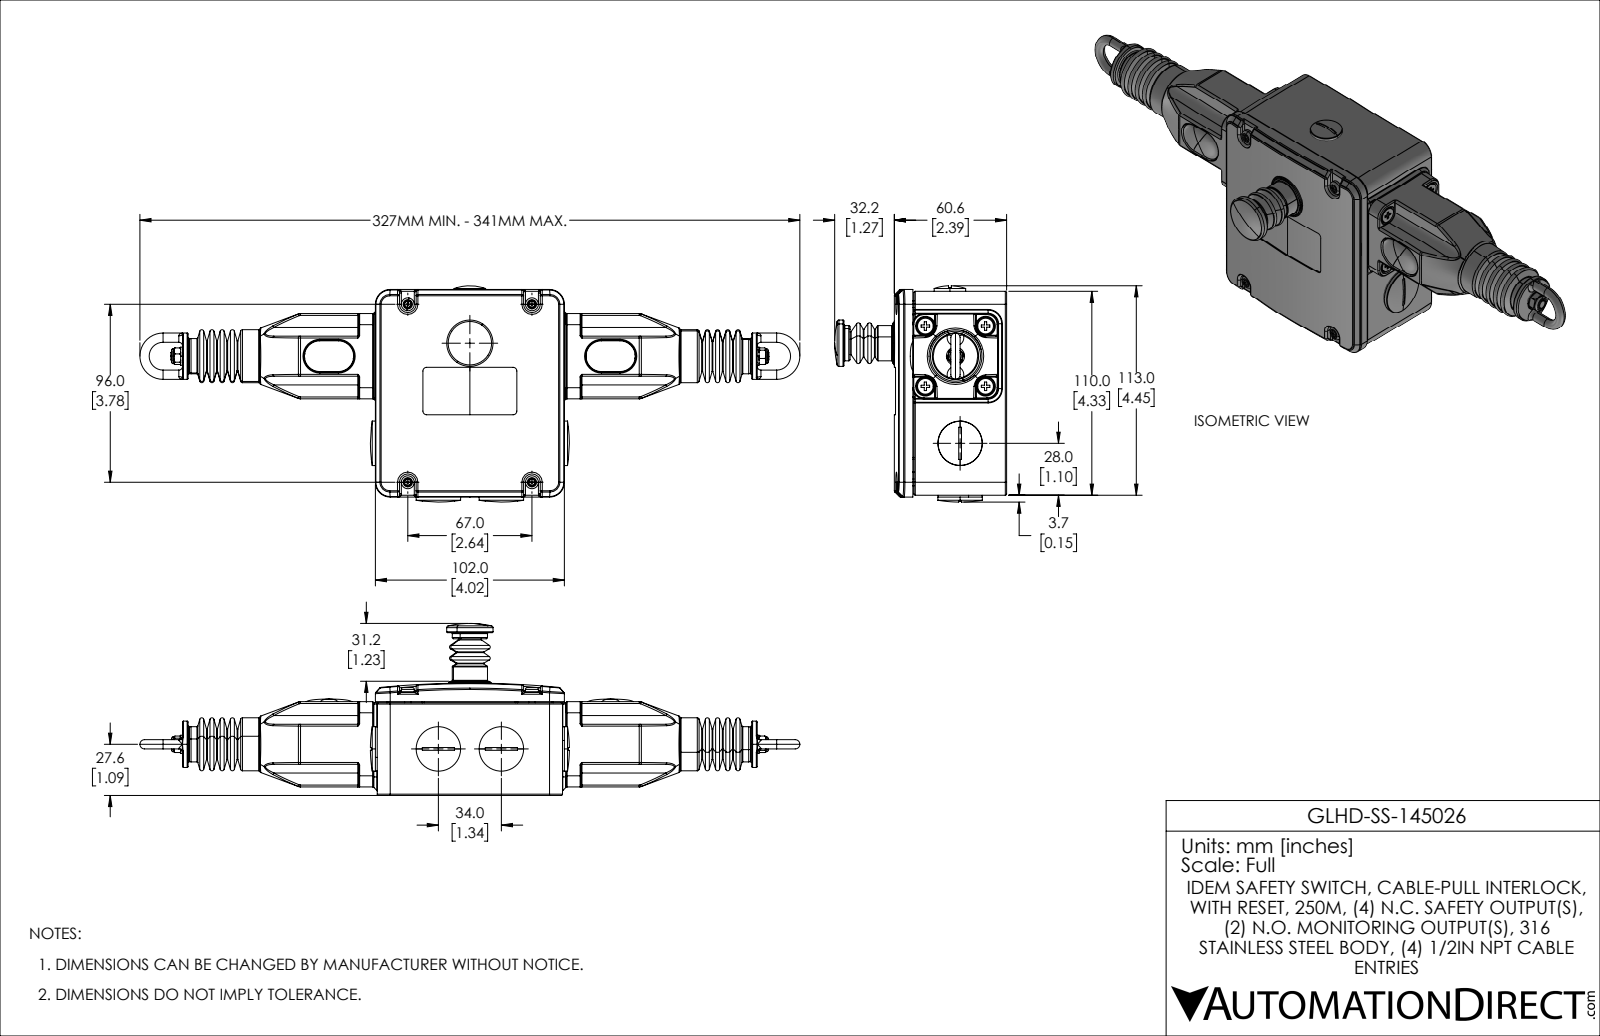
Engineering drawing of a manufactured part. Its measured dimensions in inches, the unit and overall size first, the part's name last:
Units: inches
Overall size (bounding box): 14.024 × 4.594 × 3.654
Round holes (diameter × count): ⌀0.197 ×9, ⌀0.209 ×5, ⌀0.354 ×5, ⌀0.094 ×4, ⌀0.13 ×4, ⌀0.157 ×4, ⌀0.161 ×4, ⌀0.189 ×4, ⌀0.213 ×4, ⌀0.228 ×4, ⌀0.378 ×4, ⌀0.118 ×3
Round bosses / shafts (diameter × count): ⌀0.197 ×7, ⌀0.276 ×5, ⌀0.335 ×4, ⌀0.173 ×4, ⌀0.138 ×4, ⌀0.051 ×4, ⌀0.945 ×3, ⌀0.937 ×3
Partial cylindrical surfaces — rounded edges, fillets, slot ends (radius × count): R0.02 ×252, R0.039 ×136, R0.008 ×64, R0.028 ×56, R0.012 ×18, R0.006 ×14, R0.004 ×12, R0.079 ×12
Main face-to-face distances: 0.039, 0.138, 2.181, 2.067, 0.079, 0.114, 0.157, 4.016, 0.217, 0.335
Hole centre spacings: 1.28, 0.905, 0.374, 0.902, 0.907, 1.339, 1.809, 1.891
Volume: 20.87 in³ · Surface area: 318.6 in²
Bodies: 41 solids, 4157 faces (964 planar, 1433 cylindrical, 1760 other)
Part name (STEP PRODUCT): GLHD-SS-145026
STEP written by: SolidWorks 2021 (AUTOMOTIVE_DESIGN)
